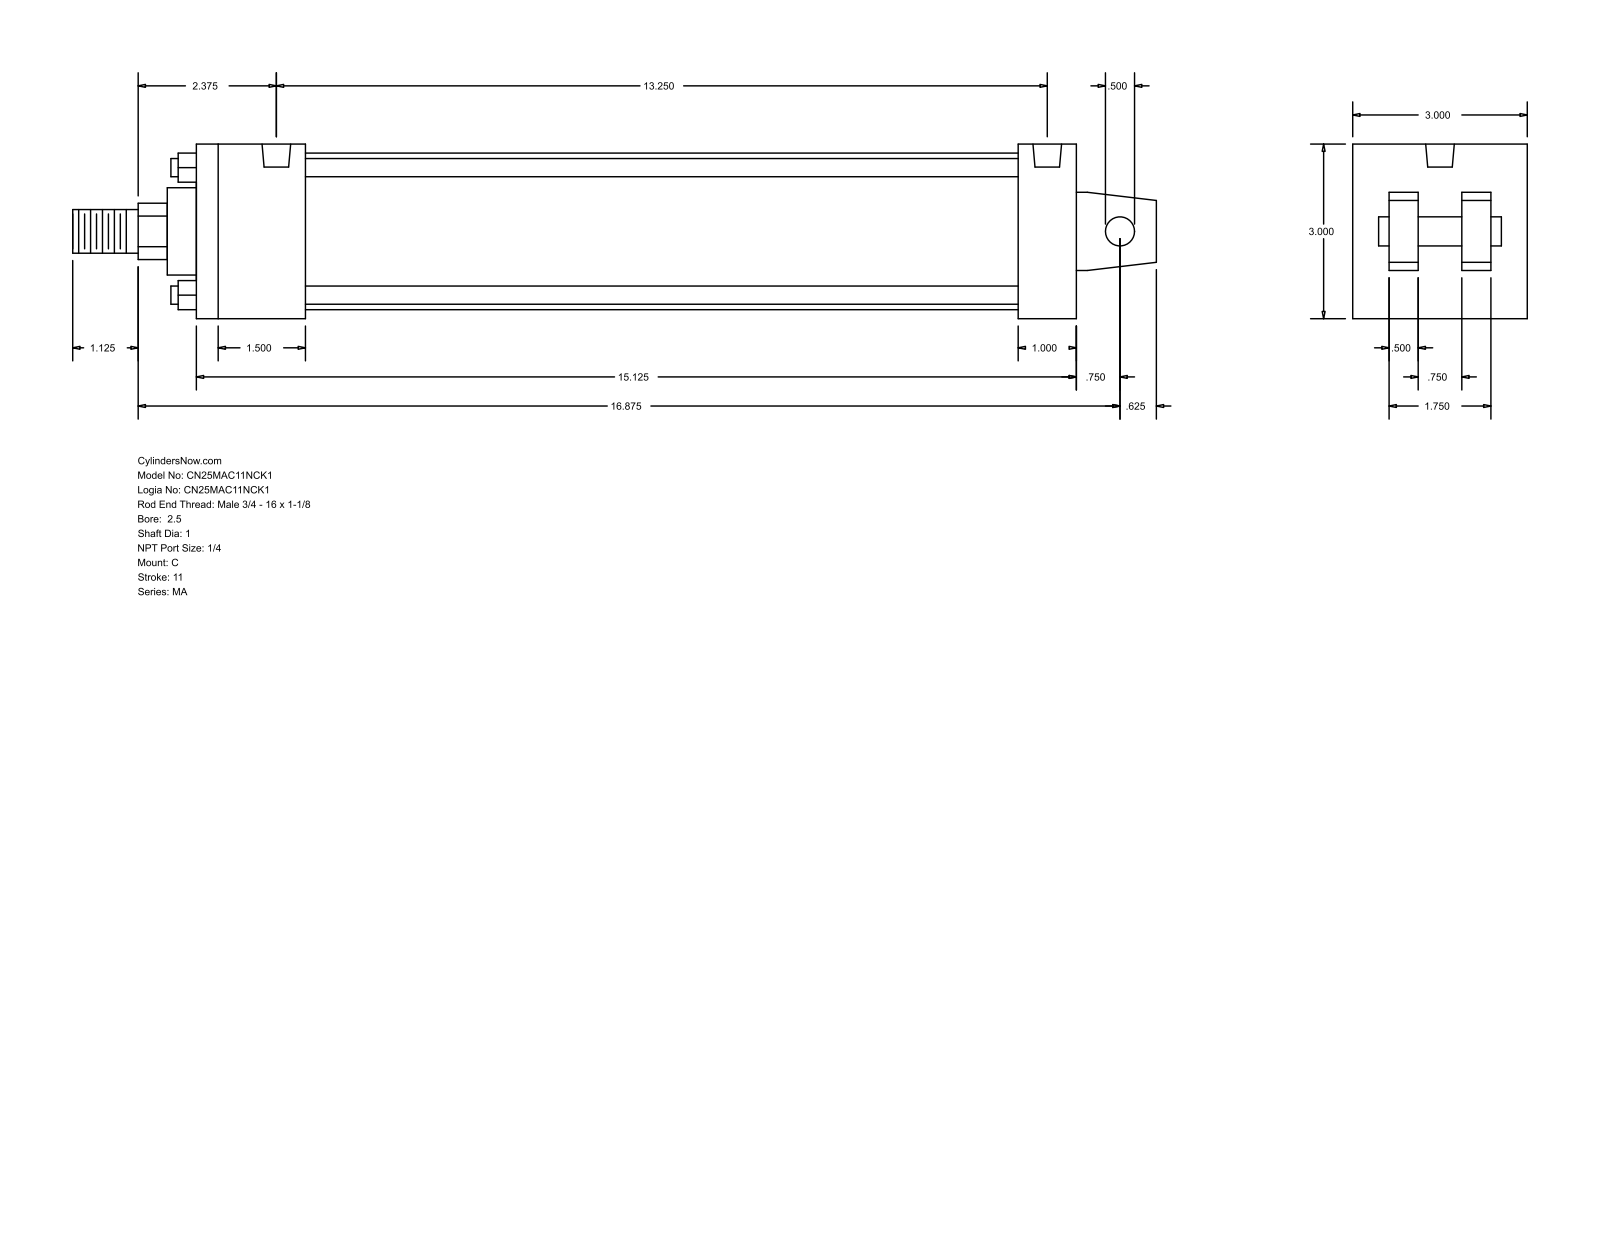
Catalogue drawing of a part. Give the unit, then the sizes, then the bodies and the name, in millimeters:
Units: millimetres
Overall size (bounding box): 473.07 × 76.2 × 76.2
Round holes (diameter × count): ⌀7.94 ×4, ⌀12.49 ×2
Round bosses / shafts (diameter × count): ⌀7.94 ×4, ⌀68.33 ×1, ⌀38.1 ×1, ⌀25.4 ×1, ⌀19.05 ×1, ⌀12.7 ×1
Partial cylindrical surfaces — rounded edges, fillets, slot ends (radius × count): R12.29 ×1
Main face-to-face distances: 76.2, 47.63, 384.17, 12.7, 60.33, 15.87, 28.57, 358.78, 311.15, 336.54
Hole centre spacings: 336.55
Bodies: 0 solids, 103 faces (76 planar, 27 cylindrical, 0 other)
Part name (STEP PRODUCT): MA_C__0250_1
STEP written by: GSSL Pune (CONFIG_CONTROL_DESIGN)
